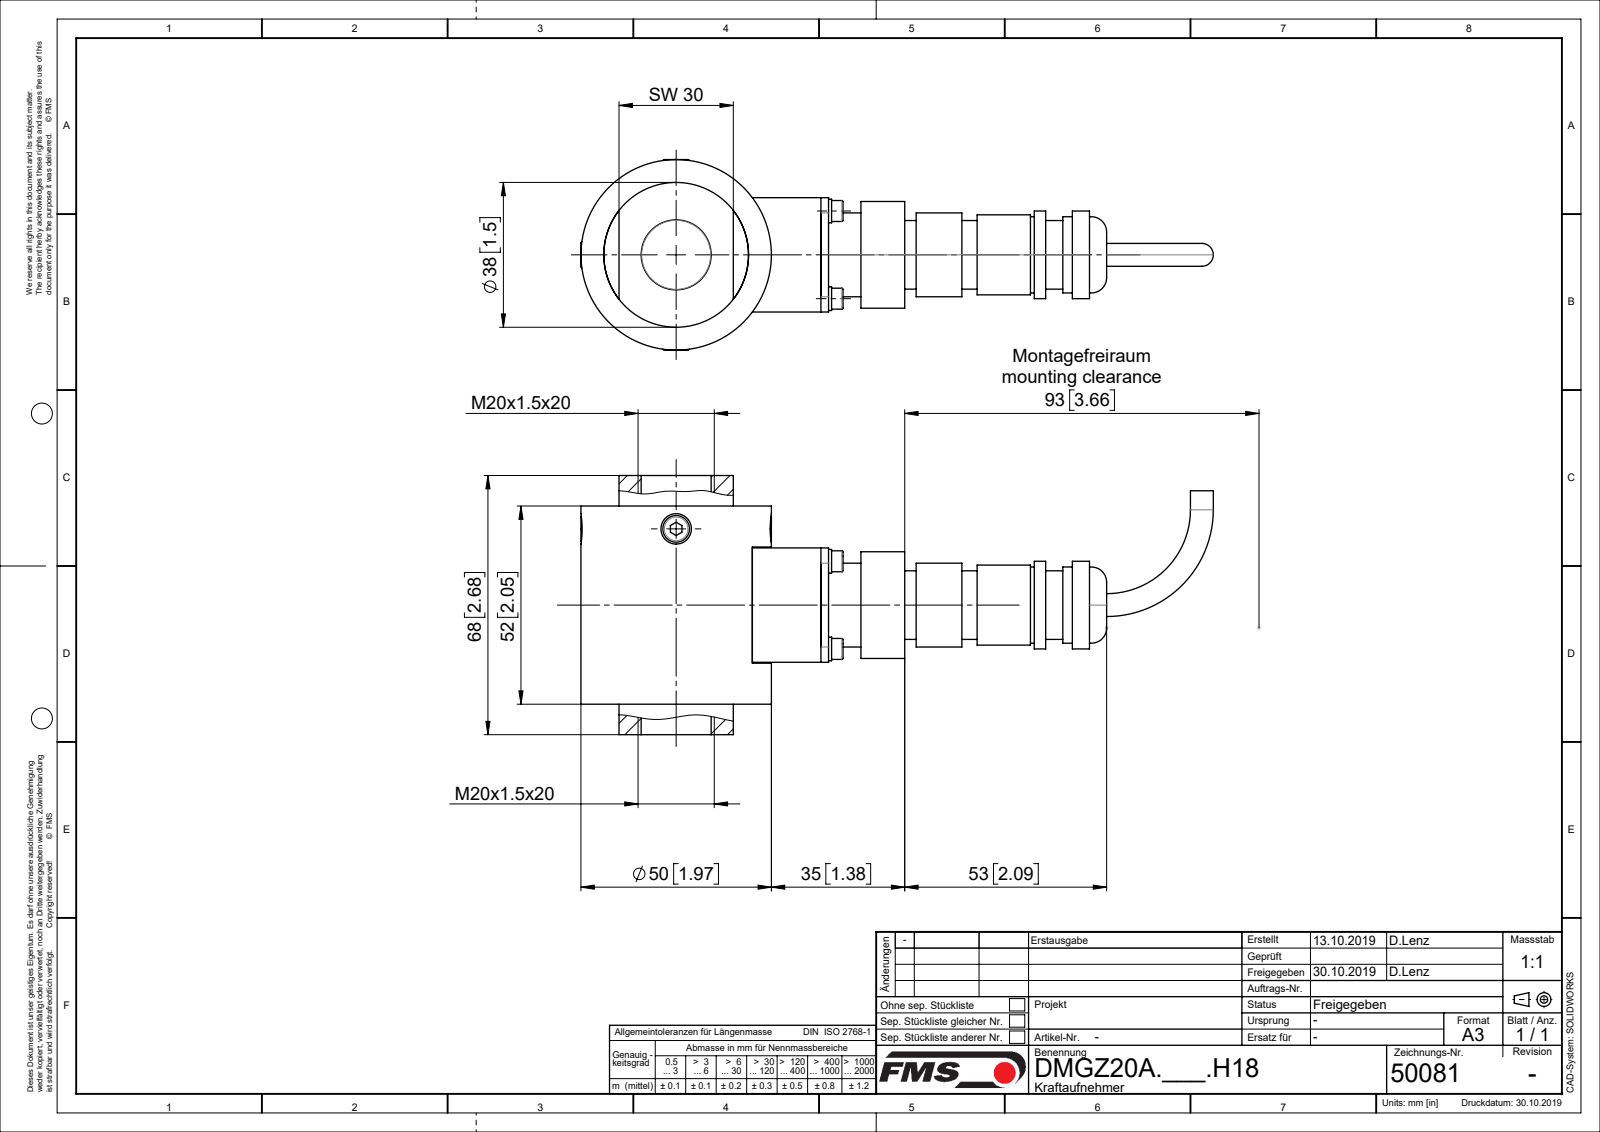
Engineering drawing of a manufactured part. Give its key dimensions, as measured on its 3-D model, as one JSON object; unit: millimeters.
{"part_name": "D50081; L49026; TEIL1; I-6KT_SCHRAUBE_M4X10 (+6 more)", "step_written_by": "Mechanical Desktop 2007 (CONFIG_CONTROL_DESIGN)", "units": "millimeters", "bodies": {"solids": 16, "faces": 287, "planar": 83, "cylindrical": 156, "other": 48}, "overall_size": [166, 84, 50], "volume_mm3": 145317, "surface_area_mm2": 46577, "round_holes": [[3.42, 6], [3.2, 4], [3.4, 4], [4.3, 2], [8, 2], [18.68, 1], [20.5, 1], [23, 1], [38, 1]], "round_bosses_or_shafts": [[6.2, 4], [5.5, 4], [3, 4], [2.5, 4], [7, 2], [4, 2], [50, 1], [28, 1]], "partial_cylinders_radius": [[4, 4]], "face_to_face_distances": [18, 60, 30, 19, 8, 41, 49, 11, 20, 52], "hole_center_spacings": [16.26, 23, 14.3, 32.53, 33.53, 20]}
